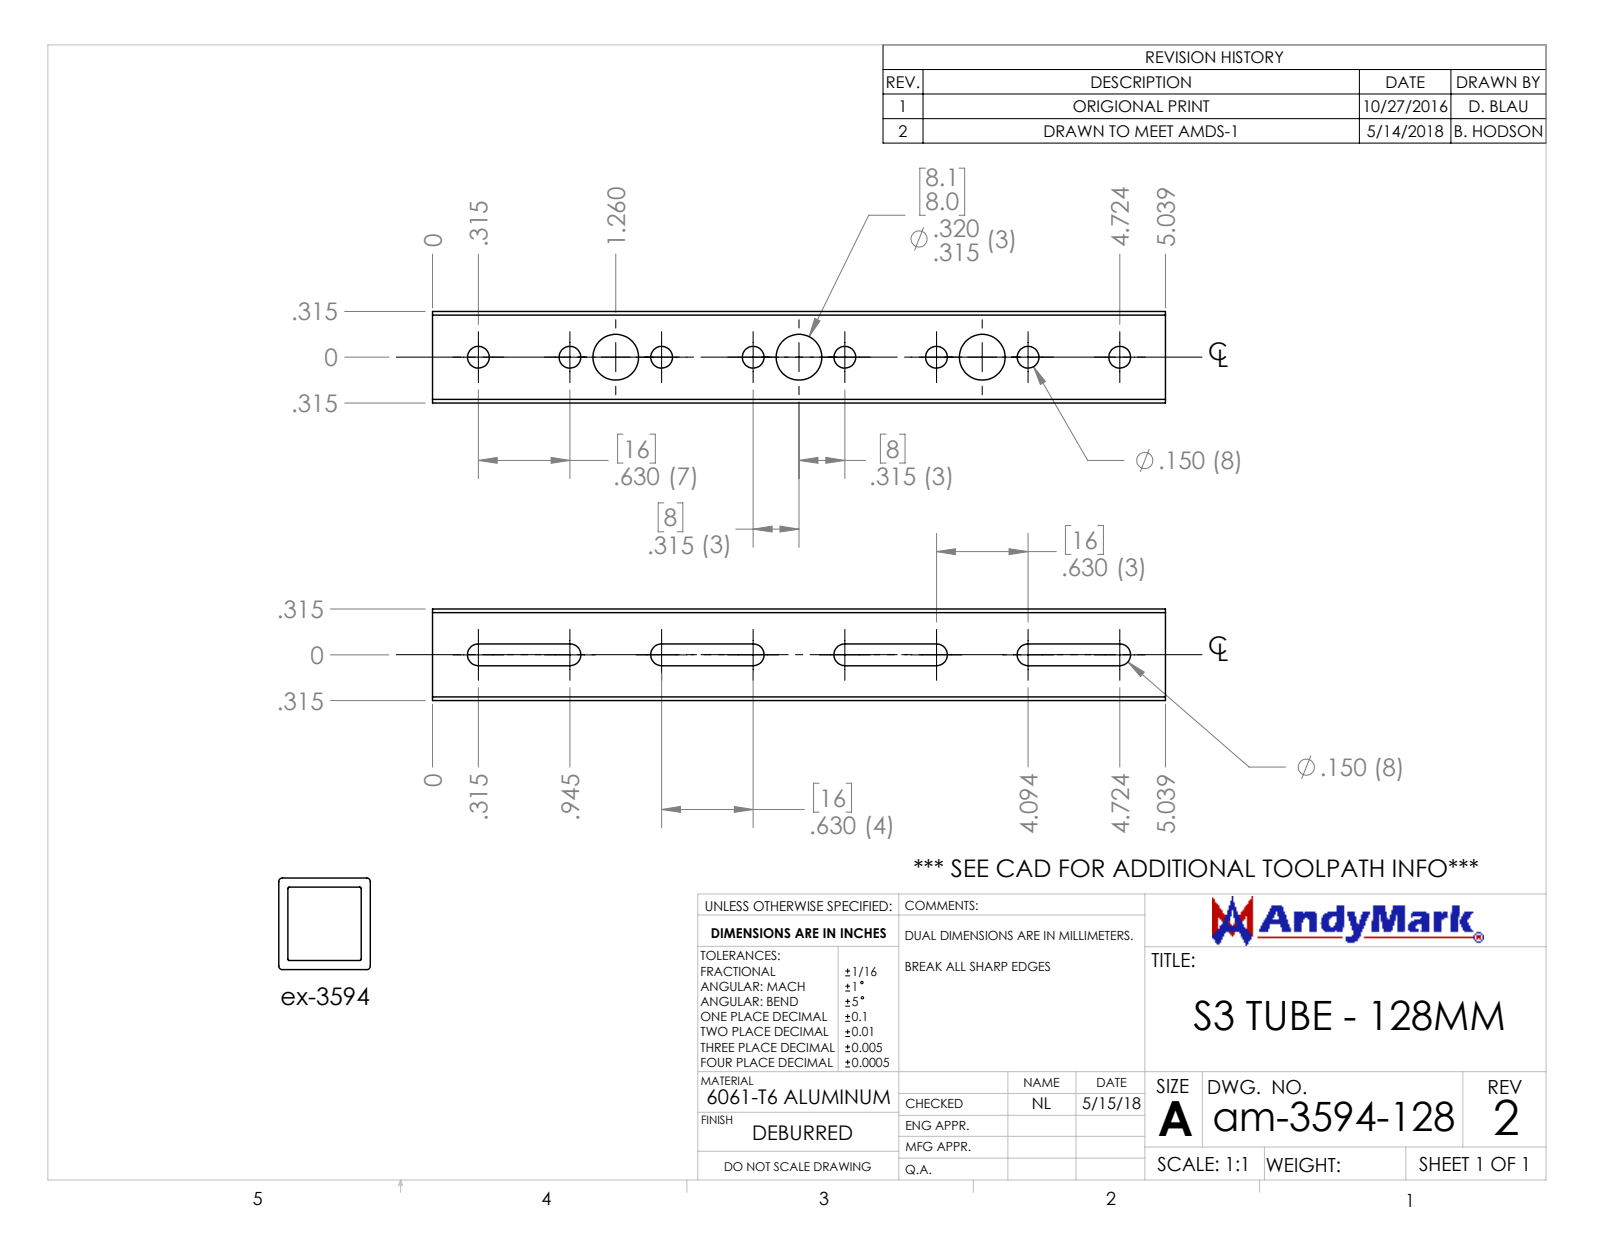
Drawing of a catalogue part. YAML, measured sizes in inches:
part_name: "am-3594-128 16mm Super Box Tubing conceptB 128mm REV2"
step_written_by: "SolidWorks 2017 (AUTOMOTIVE_DESIGN)"
units: inches
bodies: {solids: 1, faces: 102, planar: 26, cylindrical: 76, other: 0}
overall_size: [5.039, 0.63, 0.63]
volume: 0.61
surface_area: 21.27
round_holes:
  - {diameter: 0.15, count: 8}
  - {diameter: 0.315, count: 3}
partial_cylinders:
  - {radius: 0.075, count: 8}
  - {radius: 0.01, count: 4}
  - {radius: 0.025, count: 4}
face_to_face_distances: [0.063, 0.567, 0.63, 0.505, 0.24, 0.39, 0.178, 0.327, 0.39, 0.328]
hole_center_spacings: [0.63, 1.26, 1.89, 0.315, 0.945, 2.52, 1.575, 2.205]
